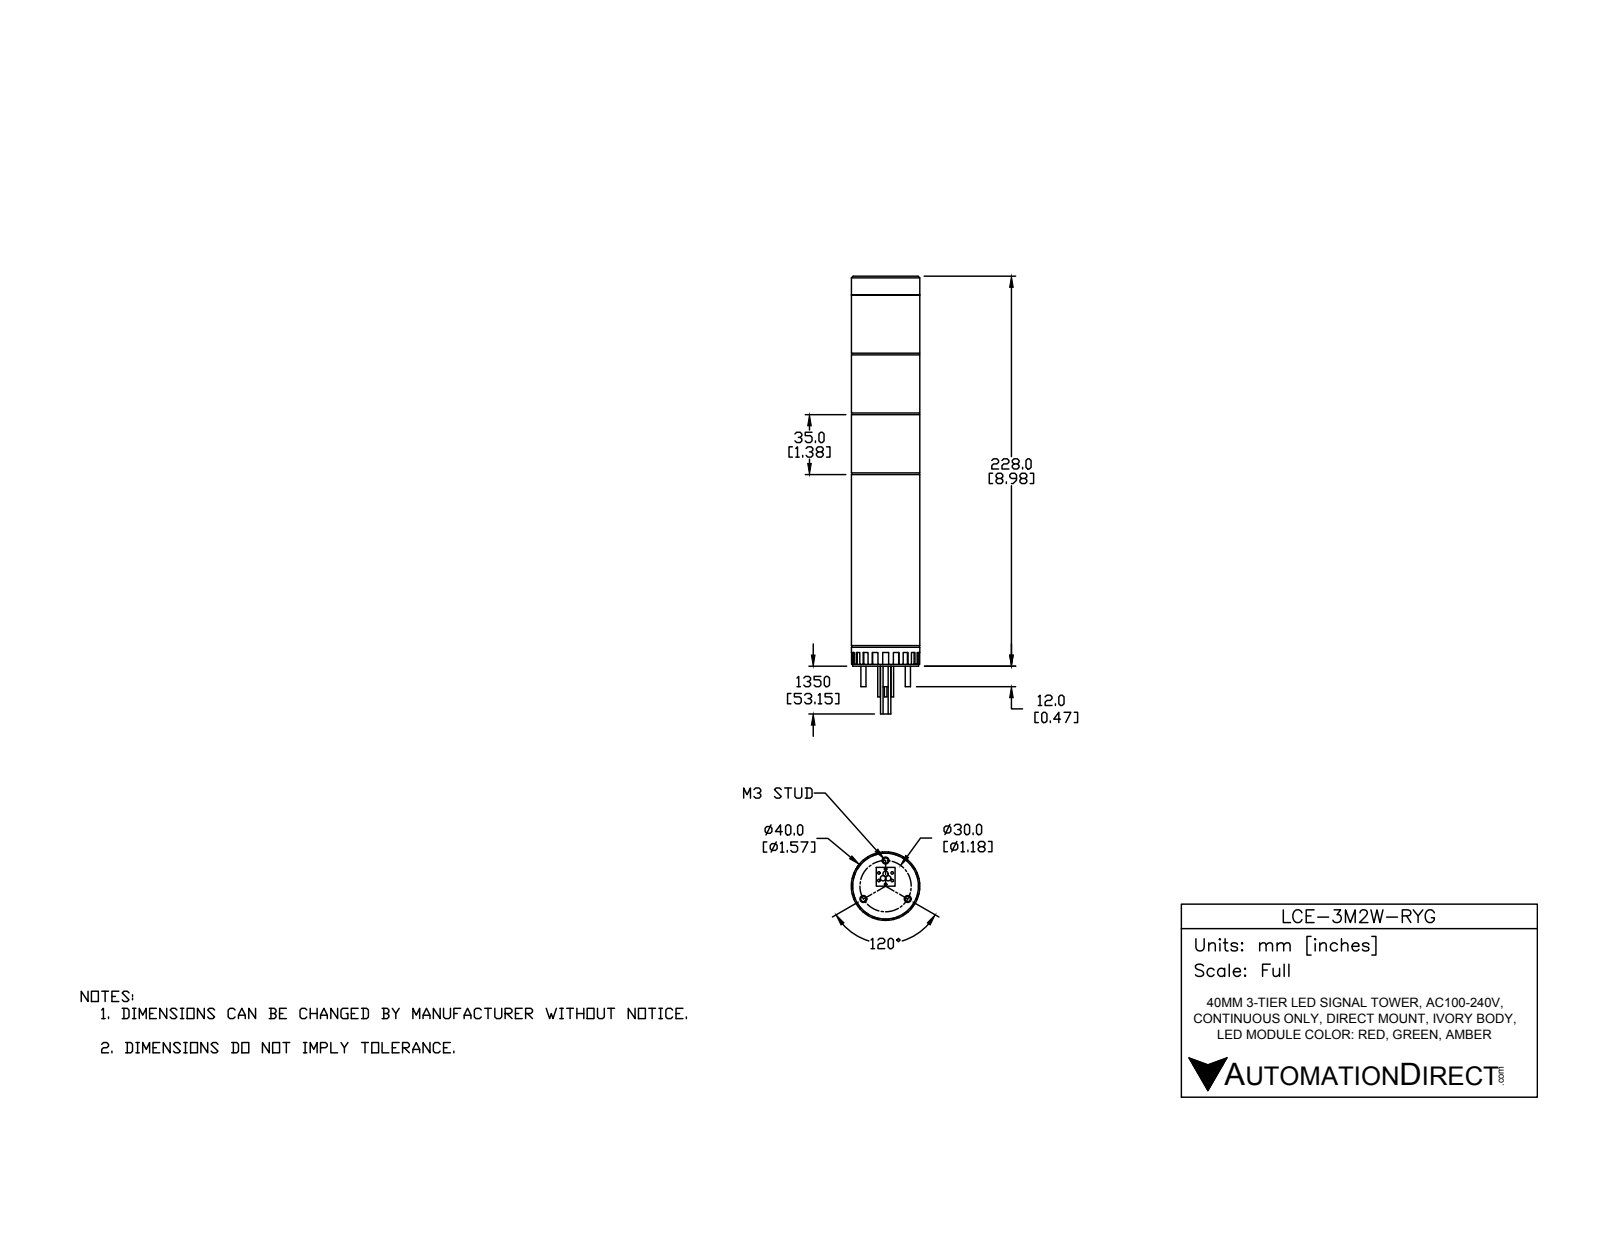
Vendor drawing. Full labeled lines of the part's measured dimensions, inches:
Part name (STEP PRODUCT): LCE-3M2W-RYG
STEP written by: SolidWorks 2016 (AUTOMOTIVE_DESIGN)
Units: inches
Bodies: 24 solids, 214 faces (154 planar, 56 cylindrical, 4 other)
Overall size (bounding box): 10.079 × 1.575 × 1.575
Volume: 17.44 in³ · Surface area: 90.4 in²
Round holes (diameter × count): ⌀0.157 ×3, ⌀0.315 ×1
Round bosses / shafts (diameter × count): ⌀0.118 ×6, ⌀0.059 ×6, ⌀1.575 ×1, ⌀1.555 ×1, ⌀1.516 ×1, ⌀0.217 ×1
Main face-to-face distances: 1.378, 0.039, 2.756, 1.339, 1.417, 2.717, 3.976, 5.354, 6.732, 0.433
Hole centre spacings: 0.591, 1.023
